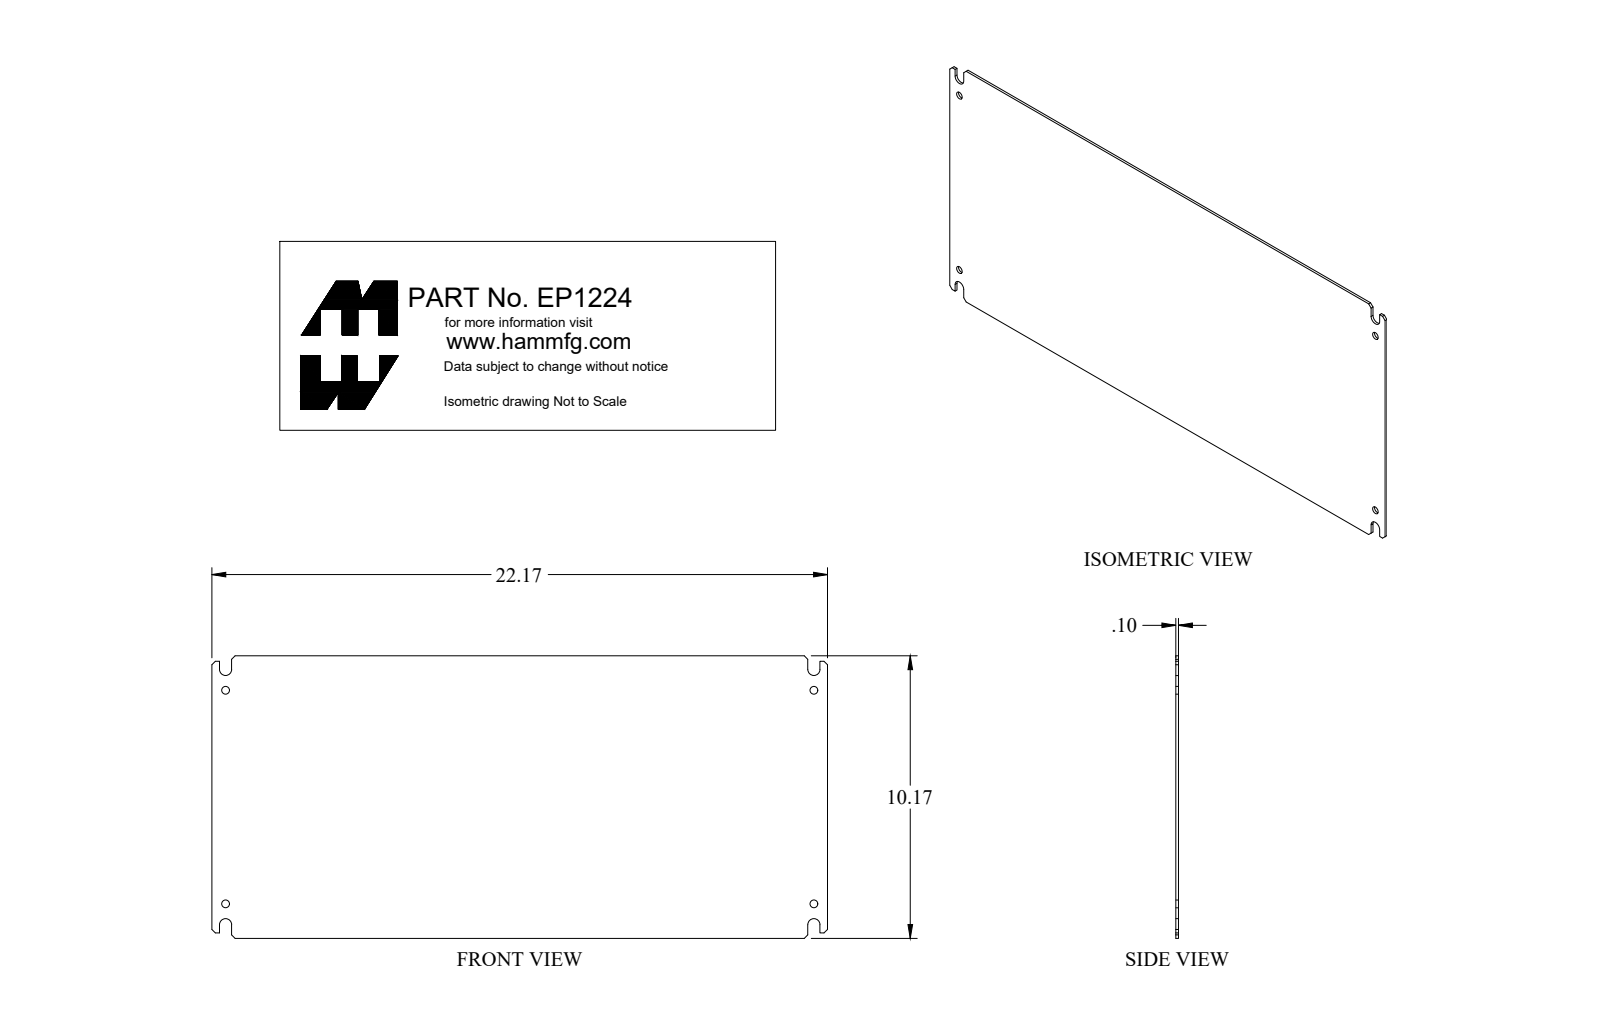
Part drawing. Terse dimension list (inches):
name: EP1224
written by: SolidWorks 2018 (AUTOMOTIVE_DESIGN)
unit: in
bodies: 1 solid, 40 faces (26 planar, 14 cylindrical, 0 other)
size: 22.17 × 10.17 × 0.095
volume: 21.26 in³; area: 454.3 in²
holes: 4× ⌀0.281
rounds: 4× R0.219
face distances: 0.095, 10.17, 22.17, 0.709, 21.461, 0.272, 21.898, 0.437, 21.188, 20.751
hole spacings: 7.688, 21.188, 22.54
